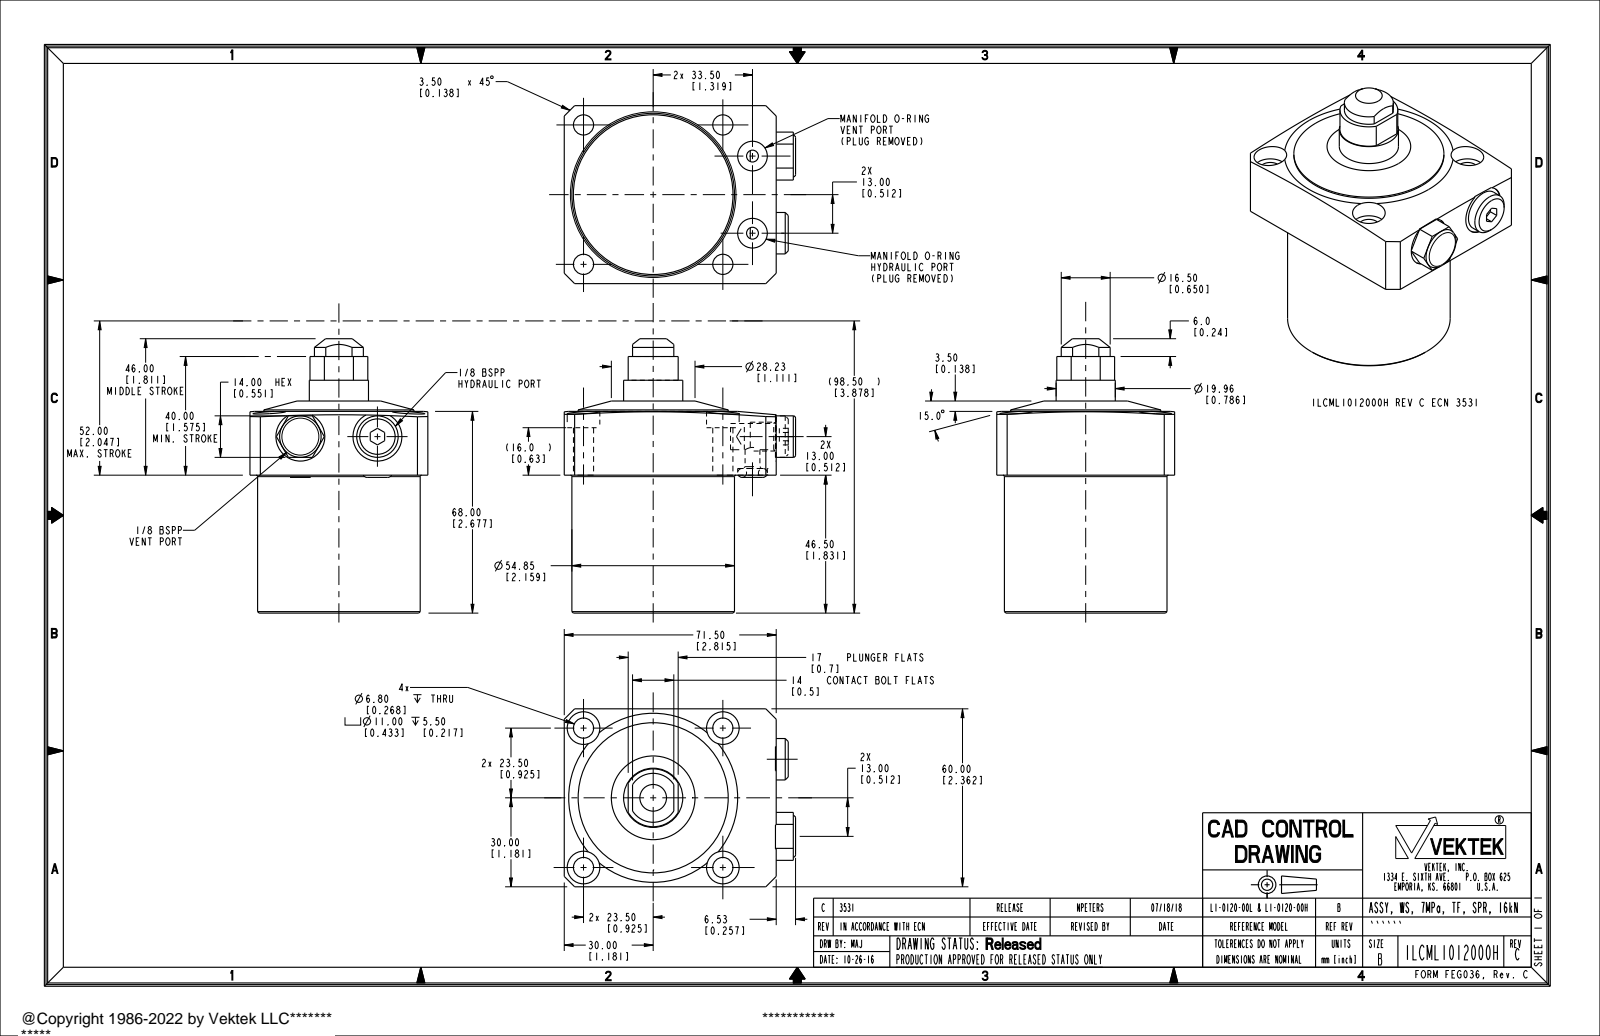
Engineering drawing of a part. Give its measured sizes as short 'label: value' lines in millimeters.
name: ILCML1012000H
written by: PRO/ENGINEER BY PARAMETRIC TECHNOLOGY CORPORATION, 2013320 (AUTOMOTIVE_DESIGN)
unit: mm
bodies: 4 solids, 137 faces (55 planar, 50 cylindrical, 32 other)
size: 92.5 × 78.03 × 60
volume: 205 838 mm³; area: 27 930 mm²
holes: 4× ⌀6.8, 4× ⌀11, 2× ⌀5, 2× ⌀6, 2× ⌀8.84, 2× ⌀10, 2× ⌀16.5
bosses: 1× ⌀54.85, 1× ⌀50.62, 1× ⌀19.96, 1× ⌀13.97, 1× ⌀9.73, 1× ⌀9.72
rounds: 1× R8.25, 1× R9.75
face distances: 46.5, 60, 71.5, 68, 21.5, 25, 3.5, 71.25, 16, 62.5
hole spacings: 47, 14.5, 26, 37.85, 57.96, 66.47, 67.68
